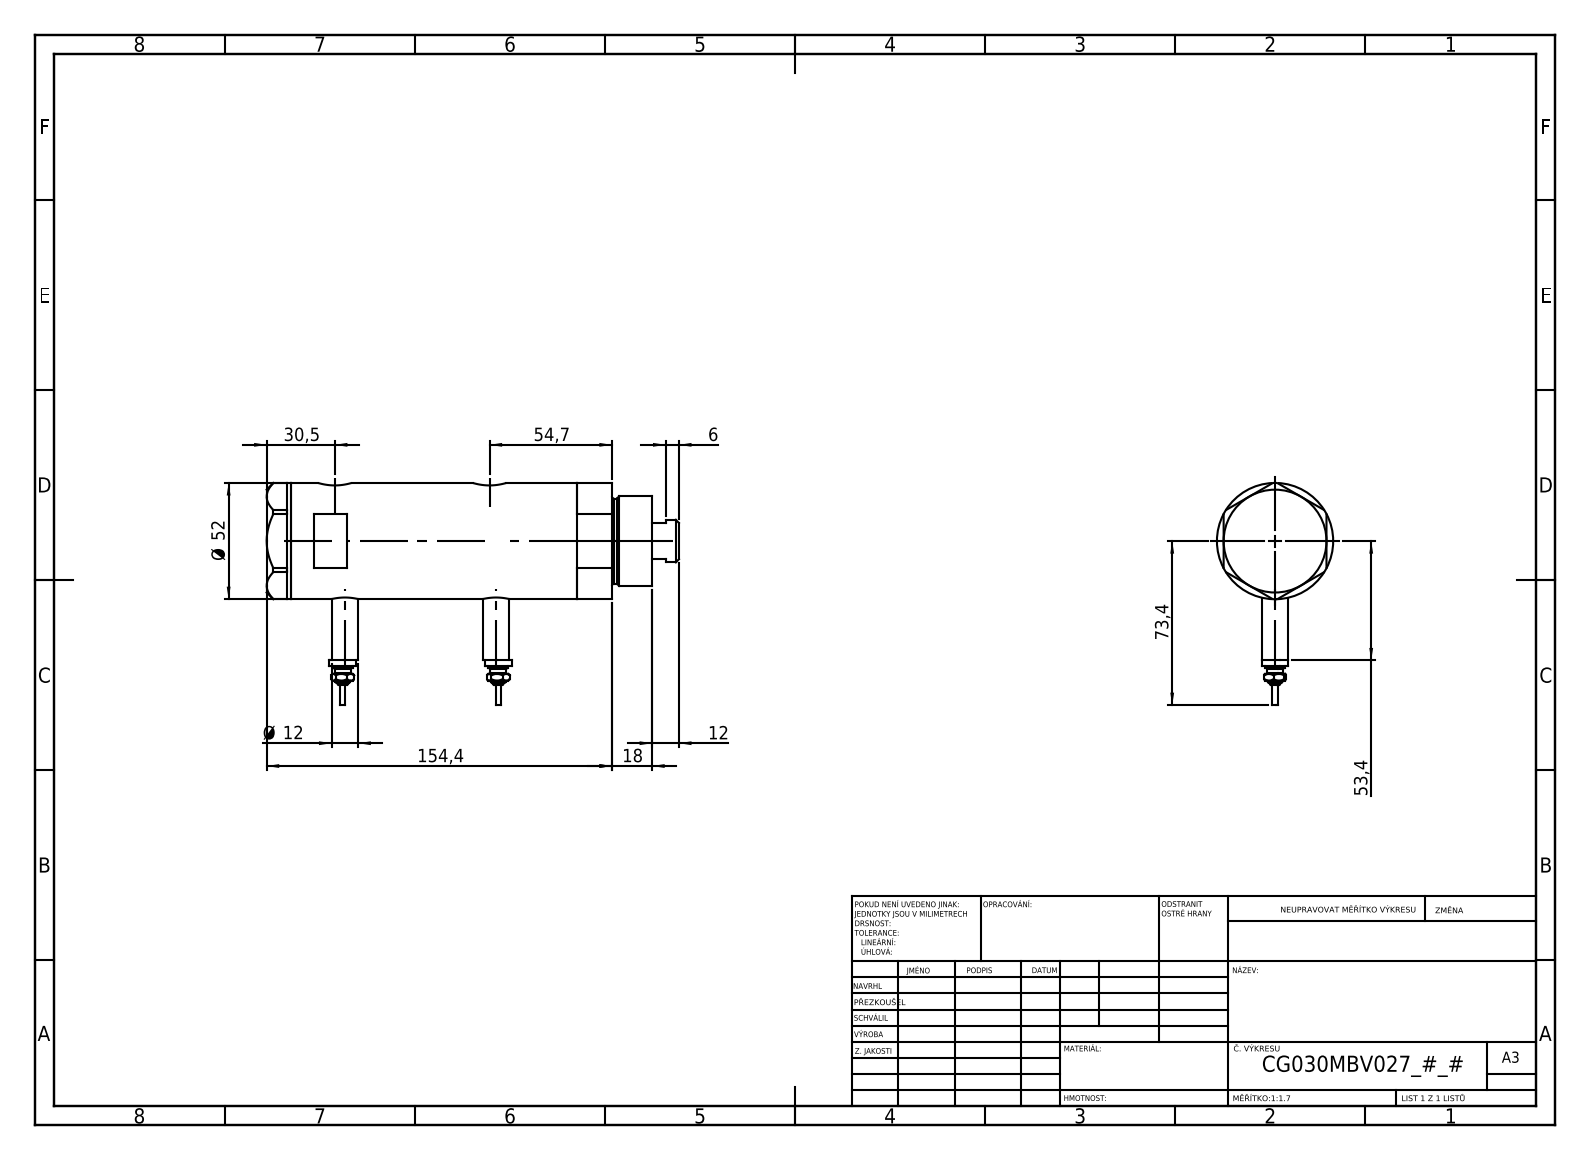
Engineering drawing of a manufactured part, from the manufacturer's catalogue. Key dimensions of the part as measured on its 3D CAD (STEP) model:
Part name (STEP PRODUCT): V270CG_FRONT; V270CG_BACK; Switch; V270CG_VC (+1 more)
STEP written by: SolidWorks 2019 (CONFIG_CONTROL_DESIGN)
Units: millimetres
Bodies: 6 solids, 226 faces (93 planar, 69 cylindrical, 64 other)
Overall size (bounding box): 184.4 × 99.4 × 52
Volume: 342 112 mm³ · Surface area: 80 007 mm²
Round holes (diameter × count): ⌀9.73 ×2, ⌀12.5 ×2, ⌀15 ×2, ⌀6.5 ×1, ⌀20 ×1, ⌀21.5 ×1, ⌀30 ×1, ⌀33 ×1, ⌀44 ×1
Round bosses / shafts (diameter × count): ⌀12 ×4, ⌀9 ×2, ⌀7 ×2, ⌀4.5 ×2, ⌀2.5 ×2, ⌀52 ×1, ⌀40 ×1, ⌀38 ×1
Main face-to-face distances: 91.5, 23.8, 67.7, 11, 34.8, 102.5, 46, 36.4, 138.9, 127.9
Hole centre spacings: 2.9, 4.5, 64.7, 67.6, 69.2, 72.1
